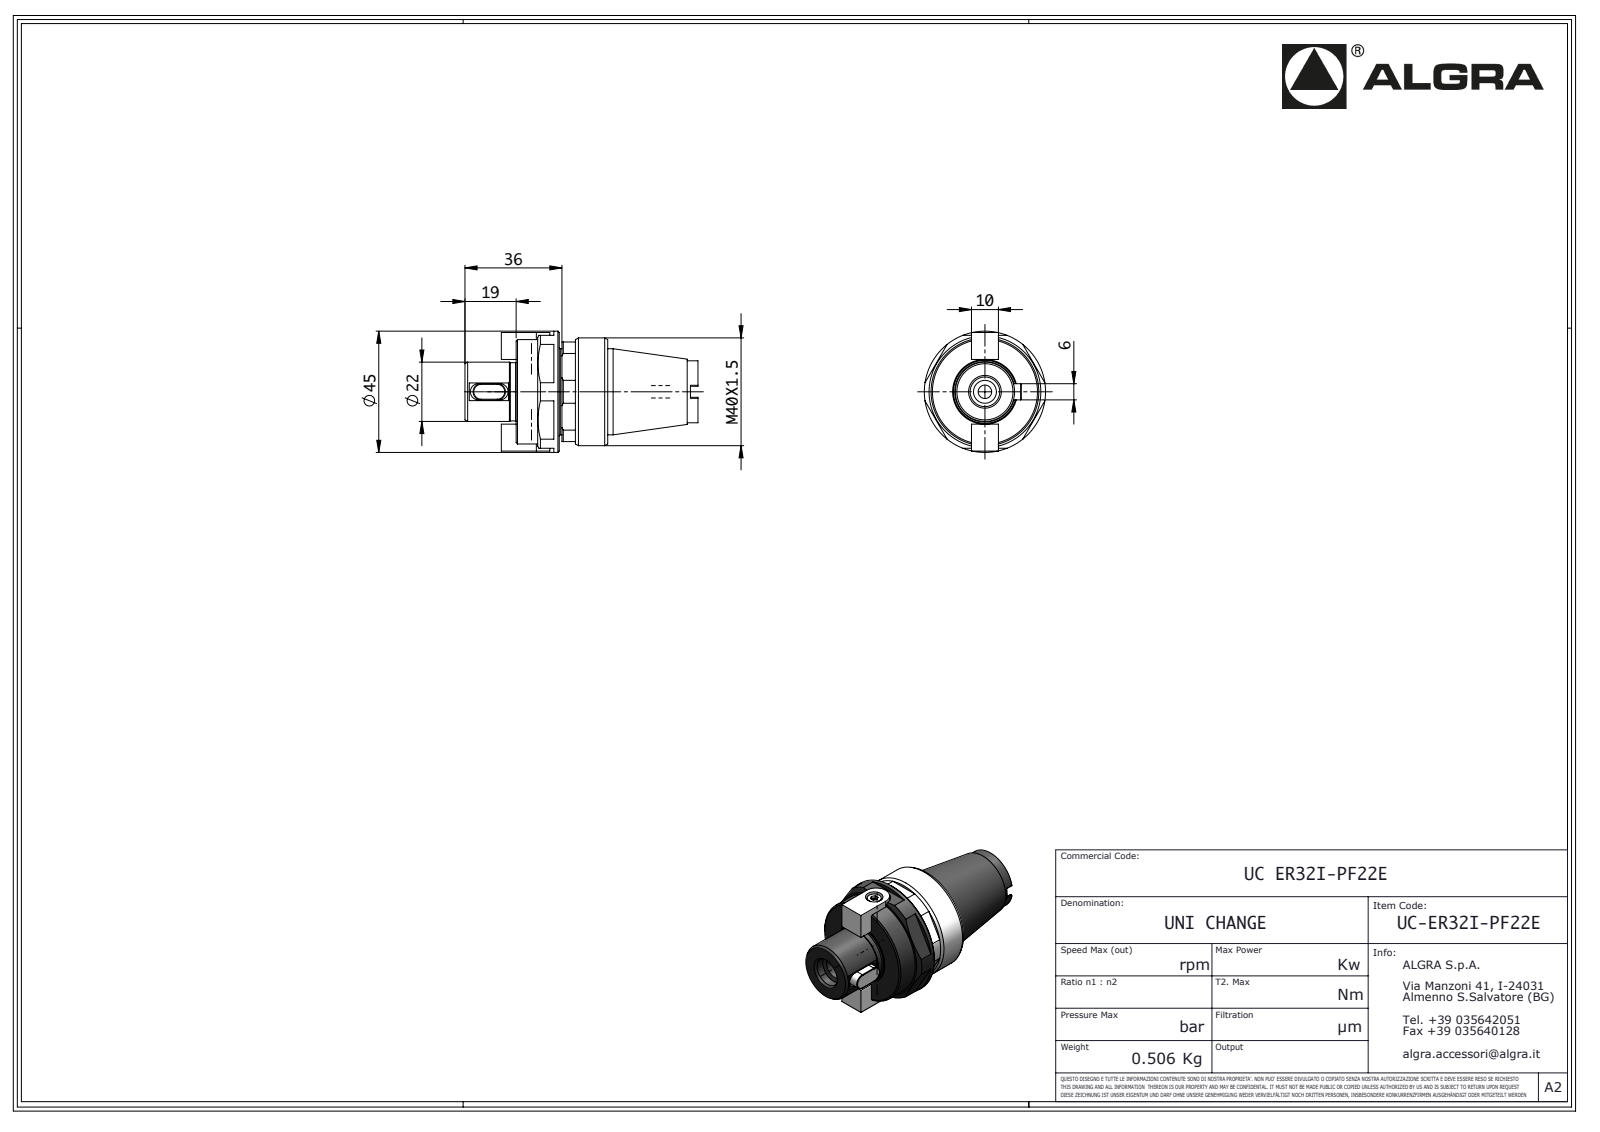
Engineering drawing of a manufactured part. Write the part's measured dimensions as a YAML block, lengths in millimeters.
part_name: "UC-ER32I-PF22E"
step_written_by: "SolidWorks 2016 (AUTOMOTIVE_DESIGN)"
units: millimeters
bodies: {solids: 0, faces: 166, planar: 86, cylindrical: 51, other: 29}
overall_size: [86.5, 45, 45]
round_holes:
  - {diameter: 1.1, count: 2}
  - {diameter: 2.5, count: 2}
  - {diameter: 1.5, count: 1}
  - {diameter: 5, count: 1}
  - {diameter: 6.5, count: 1}
  - {diameter: 8.5, count: 1}
  - {diameter: 11, count: 1}
  - {diameter: 32.05, count: 1}
round_bosses_or_shafts:
  - {diameter: 1.7, count: 2}
  - {diameter: 45, count: 1}
  - {diameter: 40, count: 1}
  - {diameter: 31.95, count: 1}
  - {diameter: 23, count: 1}
  - {diameter: 22, count: 1}
  - {diameter: 21.6, count: 1}
partial_cylinders:
  - {radius: 0.3, count: 8}
  - {radius: 3, count: 4}
  - {radius: 0.25, count: 2}
  - {radius: 5, count: 2}
  - {radius: 5.64, count: 2}
  - {radius: 7, count: 1}
  - {radius: 19.35, count: 1}
face_to_face_distances: [34, 16, 10, 18, 19, 2.48, 39.42, 13.5, 41.9, 53]
hole_center_spacings: [18.85, 7.25, 17.4, 14.5, 34.8]
